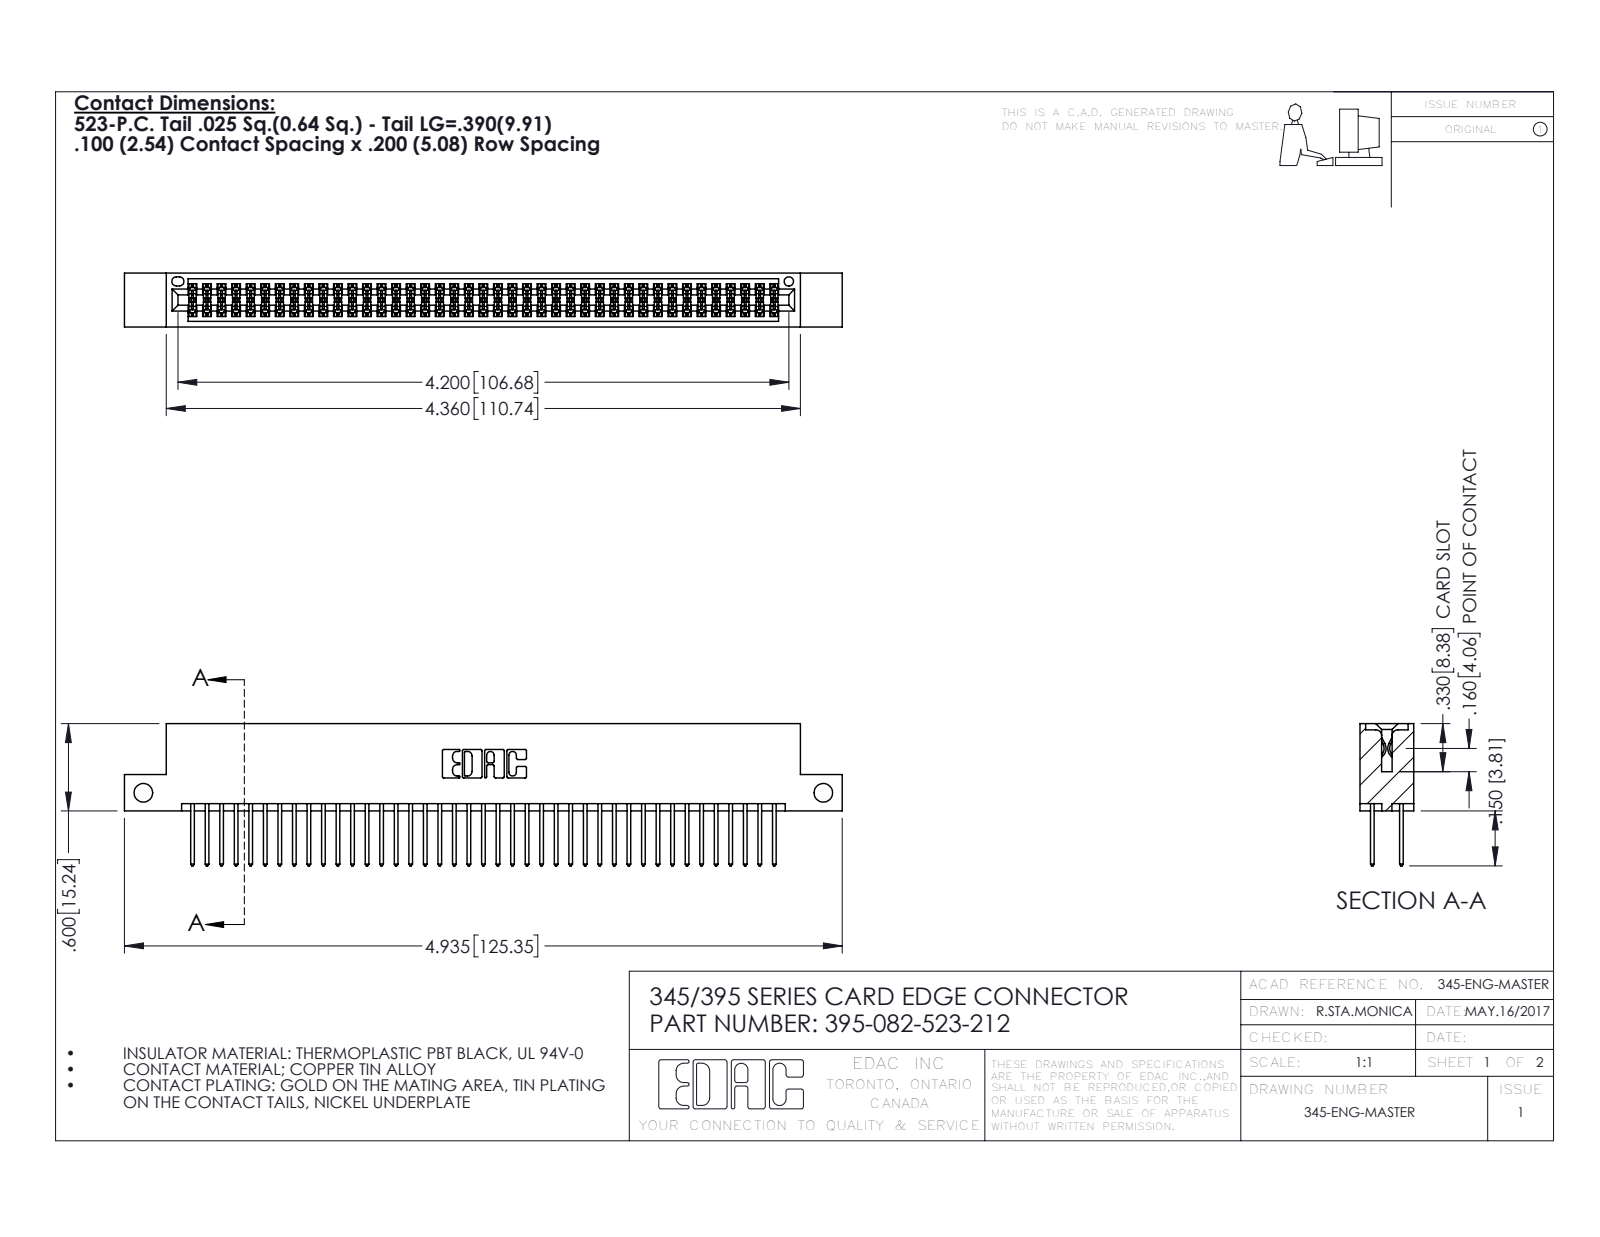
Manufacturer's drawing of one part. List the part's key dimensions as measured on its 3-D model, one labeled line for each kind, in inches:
Part name (STEP PRODUCT): 395-082-523-212; 345-292-001_345-293-123; 345 Part_Flush Mounting Lugs - Side Mount
STEP written by: SolidWorks 2016 (CONFIG_CONTROL_DESIGN)
Units: inches
Bodies: 83 solids, 4226 faces (2786 planar, 1440 cylindrical, 0 other)
Overall size (bounding box): 4.935 × 0.977 × 0.37
Volume: 0.747 in³ · Surface area: 28.99 in²
Round holes (diameter × count): ⌀0.128 ×2, ⌀0.064 ×1
Partial cylindrical surfaces — rounded edges, fillets, slot ends (radius × count): R0.006 ×123, R0.01 ×82, R0.01 ×22, R0.007 ×6, R0.031 ×6, R0.026 ×3, R0.014 ×2, R0.019 ×2
Main face-to-face distances: 0.298, 0.072, 0.2, 0.098, 0.272, 0.025, 0.37, 0.225, 0.175, 0.149
Hole centre spacings: 4.675
